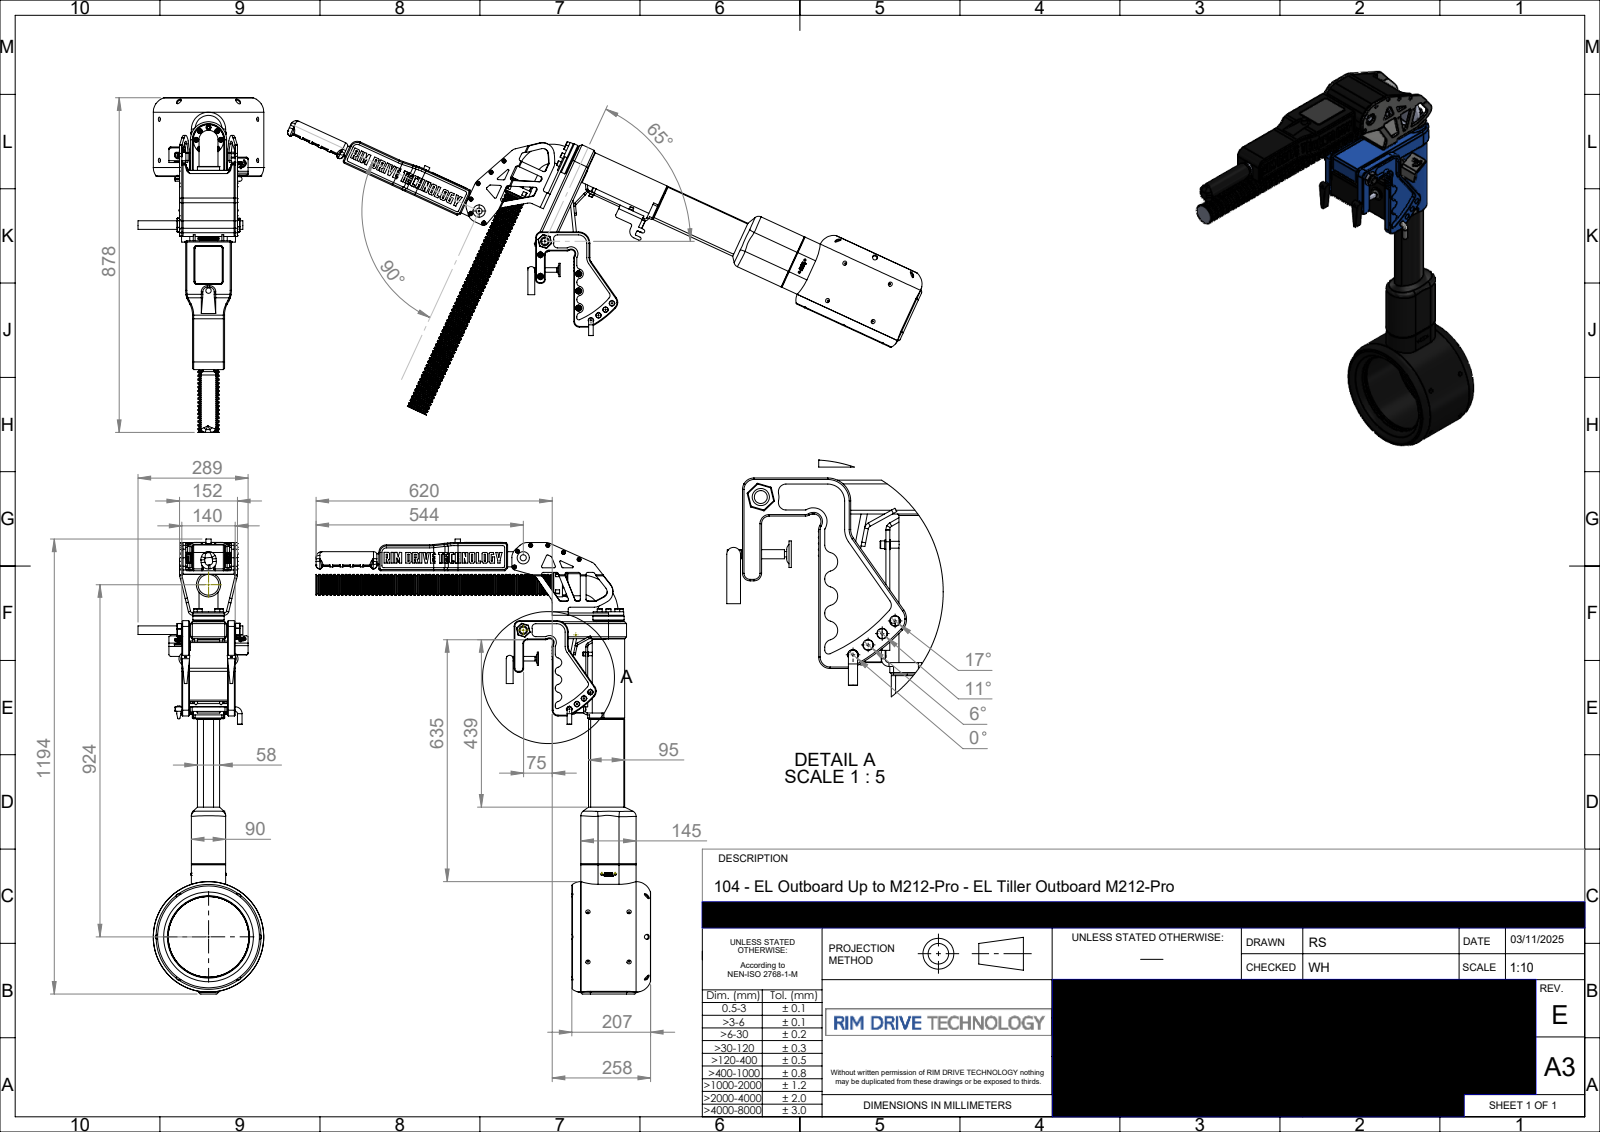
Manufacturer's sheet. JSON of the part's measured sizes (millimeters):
{"part_name": "P-104-250-rev-A-212-Pro", "step_written_by": "SolidWorks 2024 (AUTOMOTIVE_DESIGN)", "units": "millimeters", "bodies": {"solids": 1, "faces": 3787, "planar": 1766, "cylindrical": 747, "other": 1274}, "overall_size": [1193.7, 878.12, 330], "volume_mm3": 18310000, "surface_area_mm2": 1516000, "round_holes": [[4.2, 6], [5, 5], [13, 4], [5.3, 2], [4, 1], [17, 1], [32, 1], [85, 1], [212, 1], [213, 1]], "round_bosses_or_shafts": [[13, 8], [9.64, 8], [12, 7], [10, 4], [8.1, 3], [35, 2], [6.95, 2], [6, 2]], "partial_cylinders_radius": [[3, 60], [5, 50], [0.5, 43], [10, 34], [2, 26], [1, 25], [6, 12], [15, 7]], "face_to_face_distances": [10, 6, 5, 20, 120, 100, 15, 110, 95, 2.5], "hole_center_spacings": [108, 239.77, 23.7, 47.35, 54, 61.28, 732.16, 23.71]}
